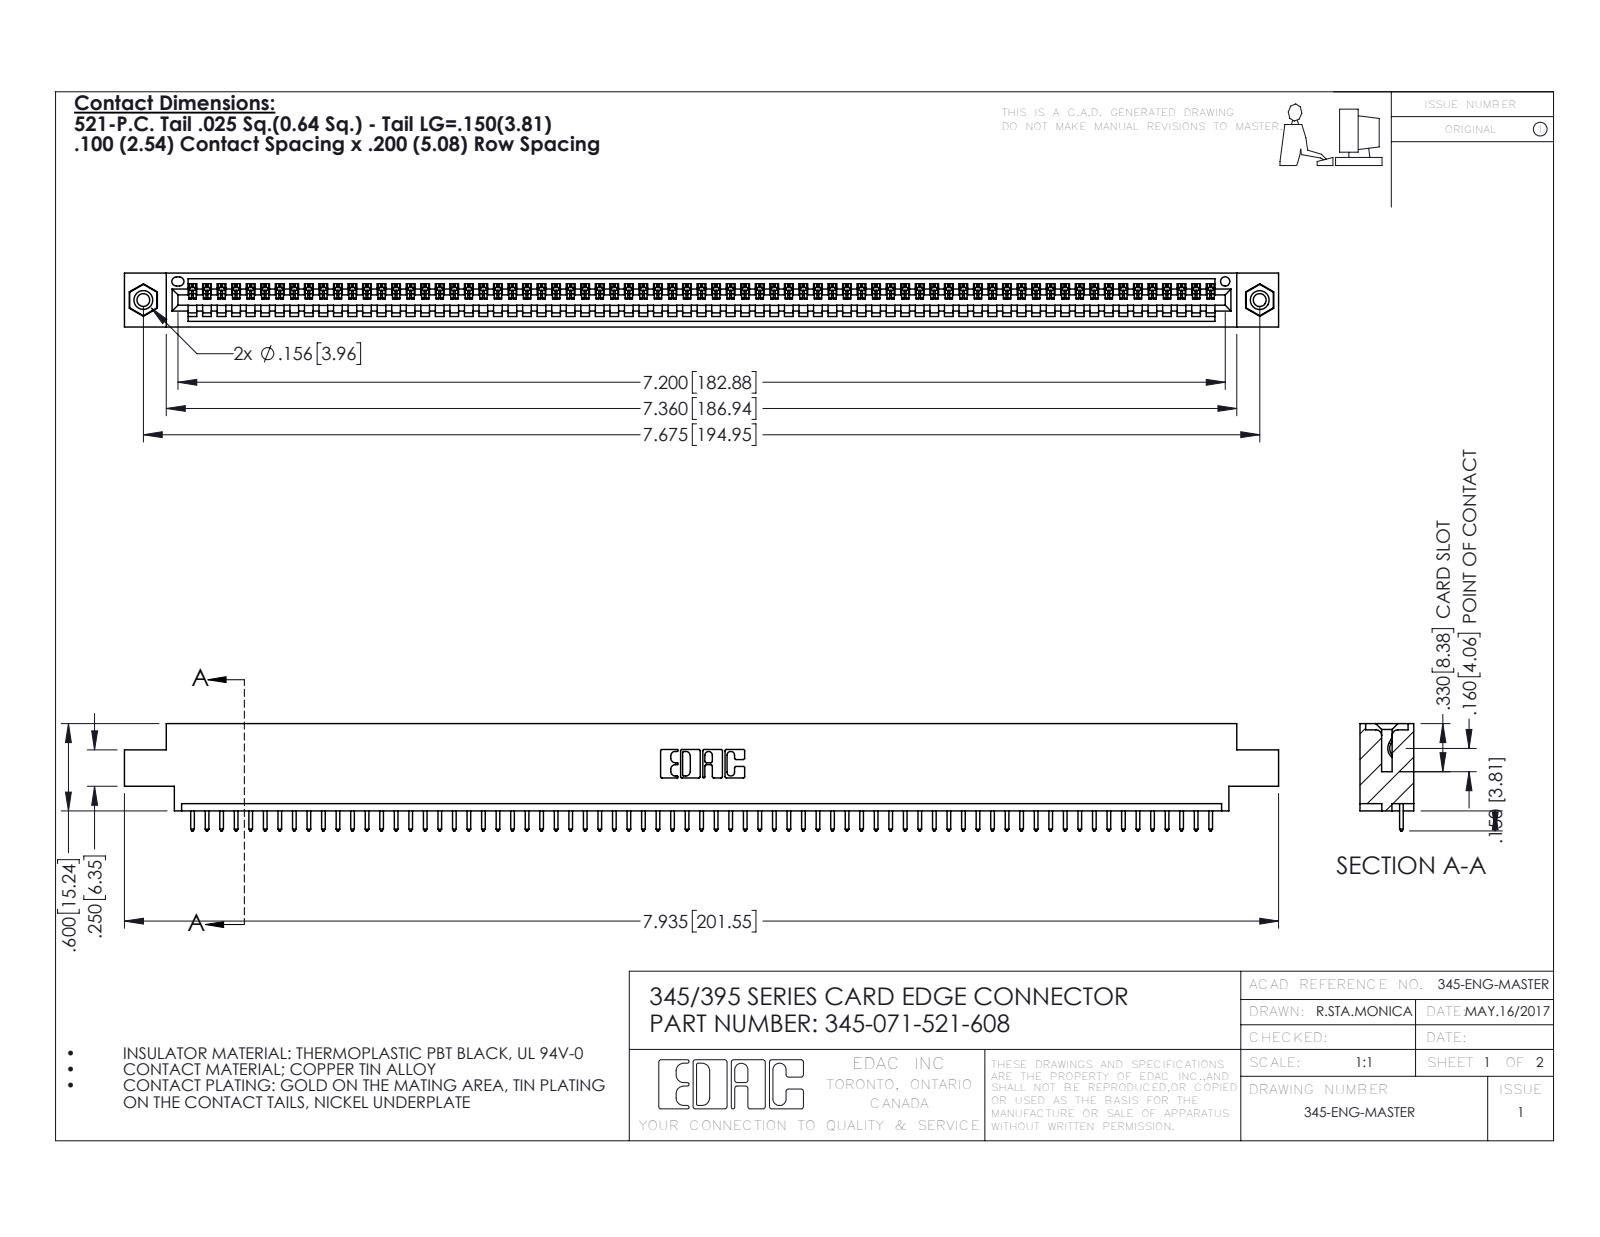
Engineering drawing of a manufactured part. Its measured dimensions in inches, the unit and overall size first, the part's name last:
Units: inches
Overall size (bounding box): 7.935 × 0.737 × 0.37
Round holes (diameter × count): ⌀0.089 ×2, ⌀0.125 ×2, ⌀0.156 ×2, ⌀0.064 ×1
Round bosses / shafts (diameter × count): ⌀0.155 ×2
Partial cylindrical surfaces — rounded edges, fillets, slot ends (radius × count): R0.006 ×142, R0.01 ×142, R0.01 ×22, R0.007 ×6, R0.031 ×6, R0.026 ×3, R0.031 ×2, R0.04 ×2
Main face-to-face distances: 0.072, 0.298, 0.37, 0.2, 0.098, 0.272, 0.025, 0.225, 0.175, 0.149
Hole centre spacings: 0.27, 7.439, 7.675
Volume: 1.163 in³ · Surface area: 38.87 in²
Bodies: 74 solids, 4308 faces (2956 planar, 1336 cylindrical, 16 other)
Part name (STEP PRODUCT): 345-292-001_345-293-121; 345-250-001_345-250-003-102; 345-071-521-608; 345 Part_0.170 Offset - 0.156 Dia-TI
STEP written by: SolidWorks 2016 (CONFIG_CONTROL_DESIGN)
